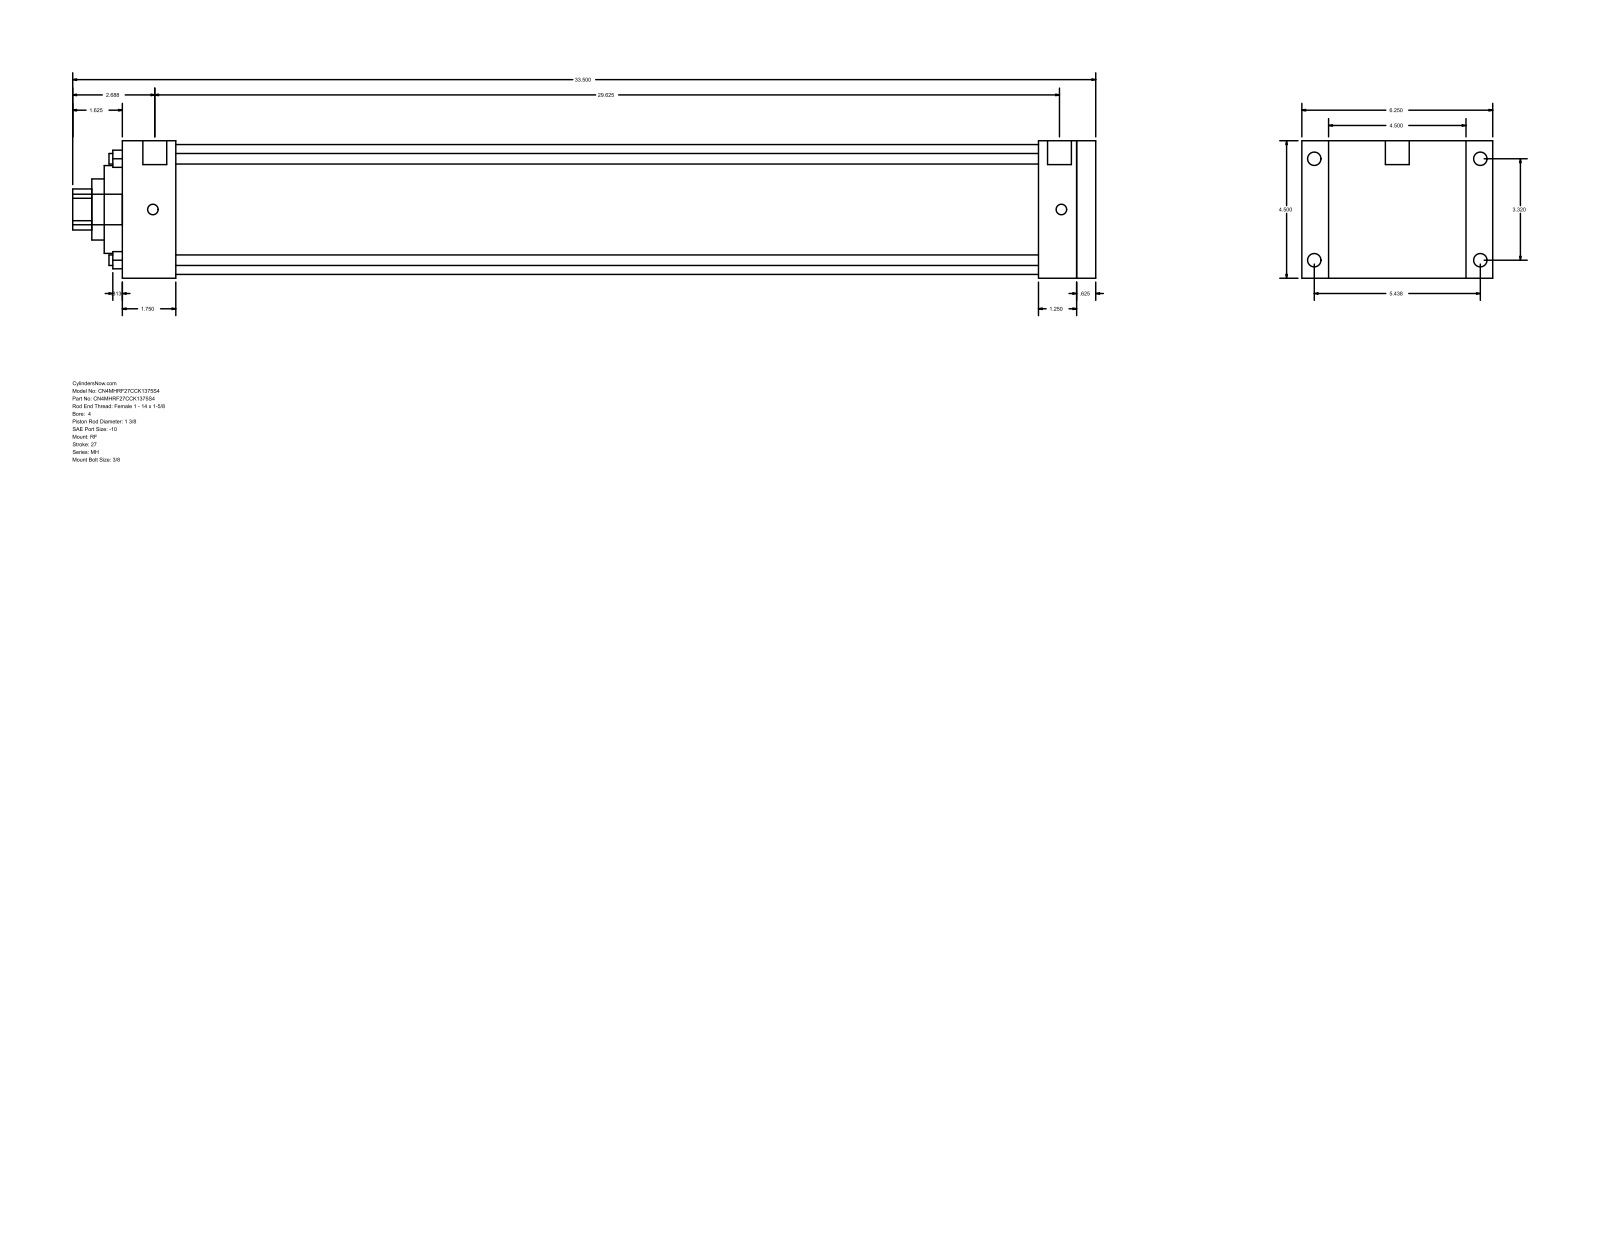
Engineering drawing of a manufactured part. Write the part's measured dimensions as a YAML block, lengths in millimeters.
part_name: "MH_RF__0400_1.375"
step_written_by: "GSSL Pune (CONFIG_CONTROL_DESIGN)"
units: millimeters
bodies: {solids: 0, faces: 94, planar: 65, cylindrical: 29, other: 0}
overall_size: [850.9, 158.75, 114.3]
round_holes:
  - {diameter: 8.76, count: 4}
  - {diameter: 34.92, count: 1}
  - {diameter: 50.8, count: 1}
  - {diameter: 73.03, count: 1}
  - {diameter: 107.95, count: 1}
round_bosses_or_shafts:
  - {diameter: 11.13, count: 4}
  - {diameter: 8.73, count: 4}
  - {diameter: 19.84, count: 2}
  - {diameter: 25.4, count: 1}
partial_cylinders:
  - {radius: 17.06, count: 1}
face_to_face_distances: [114.3, 809.63, 15.88, 793.75, 44.45, 749.3, 765.18, 762, 717.55, 31.75]
hole_center_spacings: [59.62, 84.32, 119.25]
